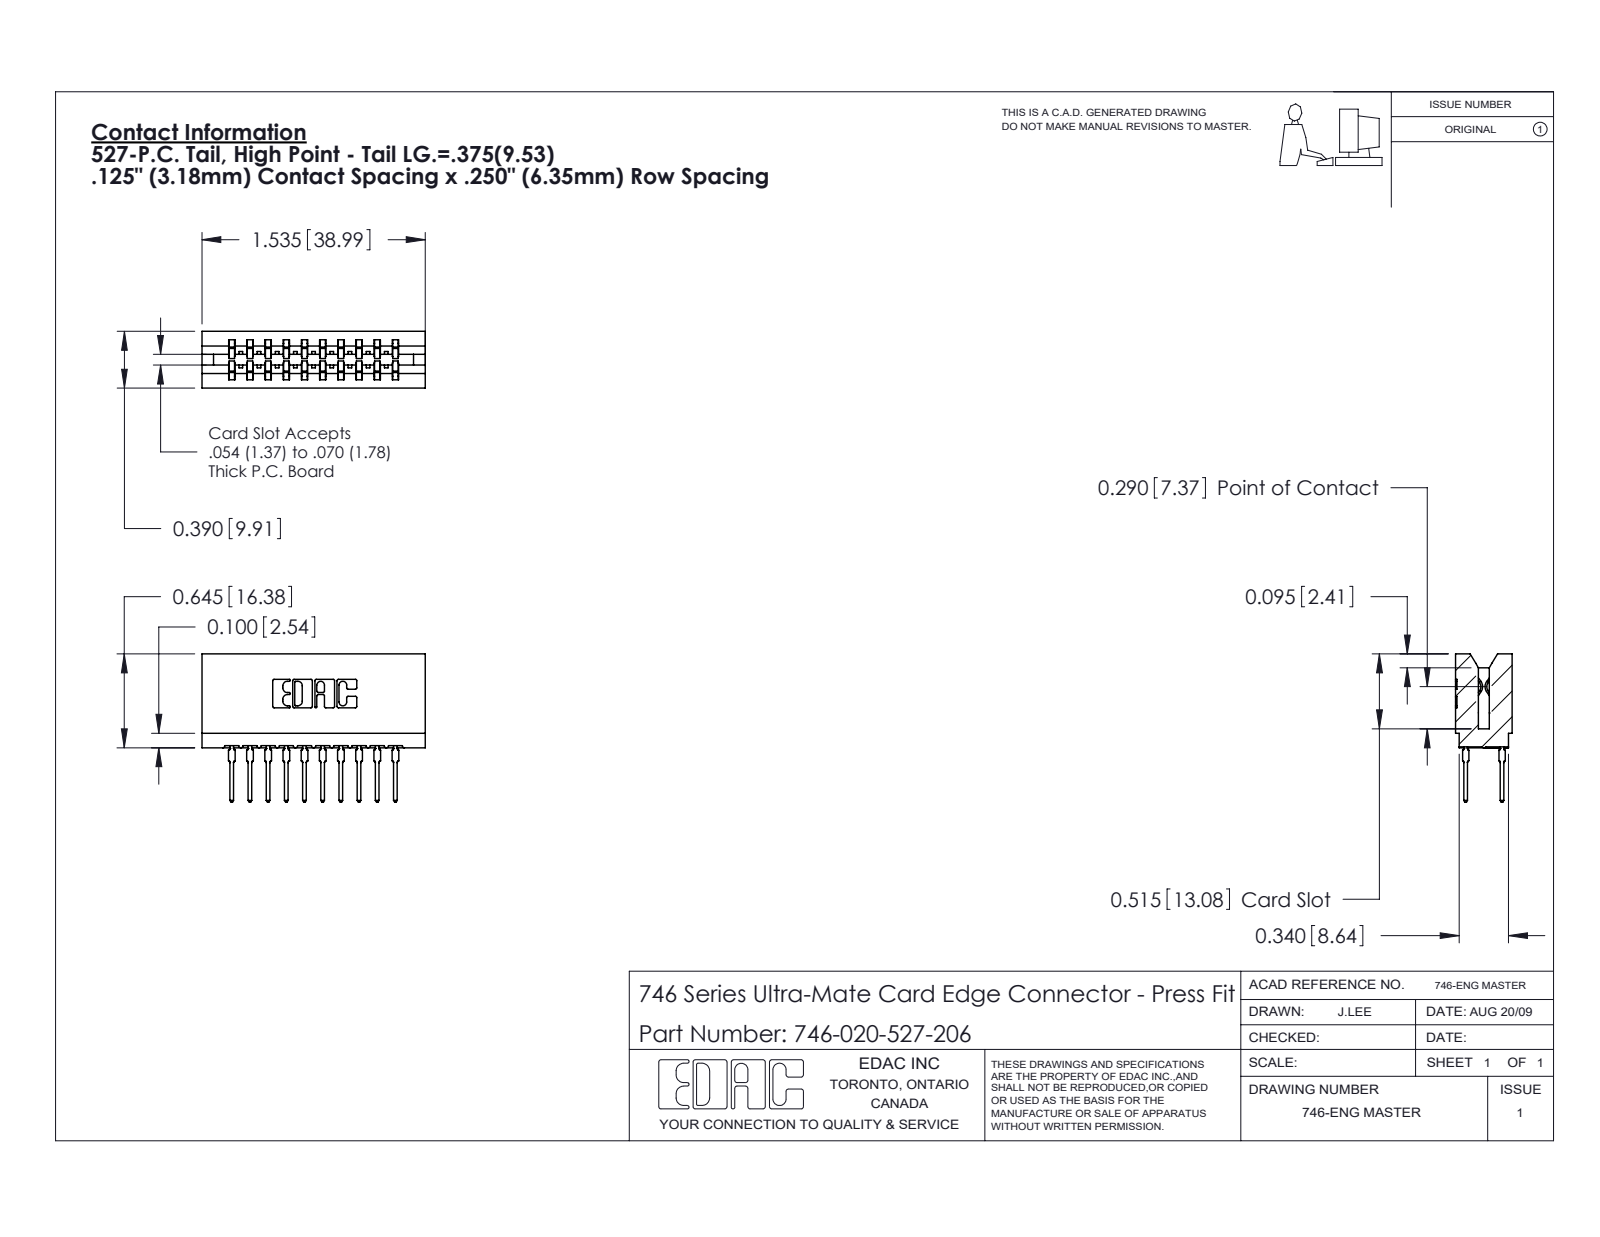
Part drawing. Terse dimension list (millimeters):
name: 746 Part_.515 Slot Depth - 06; 746-292-001_527; 746-020-527-206
written by: SolidWorks 2020 (CONFIG_CONTROL_DESIGN)
unit: mm
bodies: 21 solids, 1888 faces (976 planar, 392 cylindrical, 520 other)
size: 39 × 25.9 × 9.9
volume: 4 390 mm³; area: 6 587 mm²
rounds: 40× R0.5, 22× R0.3, 11× R0.4, 8× R0.1, 8× R0.3, 6× R0.2, 6× R0.8, 3× R0.7
face distances: 6.4, 8.5, 1.4, 12.7, 1.1, 3.2, 7.4, 19.1, 9.9, 9.5
